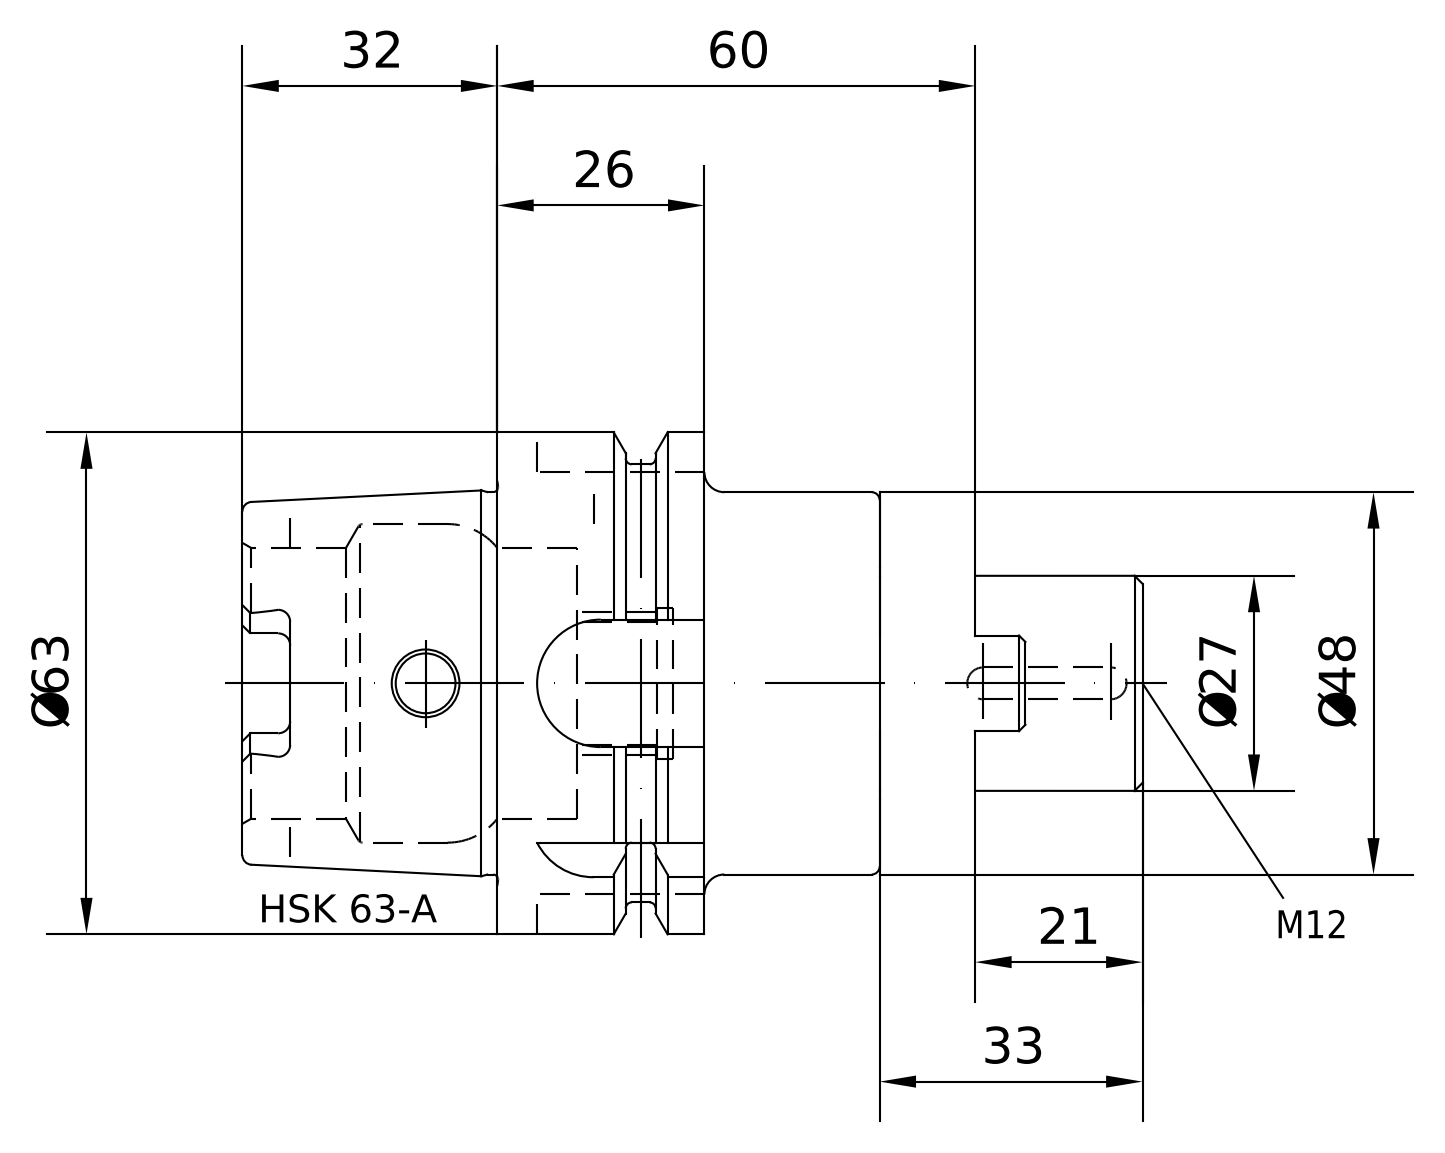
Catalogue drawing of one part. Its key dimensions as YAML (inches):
part_name: "A63-040-27; 85-200-27; A63-040-27_ASM"
step_written_by: "PRO/ENGINEER BY PARAMETRIC TECHNOLOGY CORPORATION, 2010430 (CONFIG_CONTROL_DESIGN)"
units: inches
bodies: {solids: 2, faces: 266, planar: 124, cylindrical: 64, other: 78}
overall_size: [4.449, 2.48, 2.48]
volume: 9.104
surface_area: 58.86
round_holes:
  - {diameter: 0.295, count: 1}
  - {diameter: 0.394, count: 1}
  - {diameter: 0.402, count: 1}
  - {diameter: 0.472, count: 1}
  - {diameter: 0.666, count: 1}
  - {diameter: 0.721, count: 1}
  - {diameter: 0.735, count: 1}
  - {diameter: 1.077, count: 1}
  - {diameter: 1.24, count: 1}
  - {diameter: 1.339, count: 1}
  - {diameter: 1.575, count: 1}
round_bosses_or_shafts:
  - {diameter: 2.48, count: 1}
  - {diameter: 2.165, count: 1}
  - {diameter: 1.891, count: 1}
  - {diameter: 1.89, count: 1}
  - {diameter: 1.063, count: 1}
  - {diameter: 0.709, count: 1}
partial_cylinders:
  - {radius: 0.059, count: 6}
  - {radius: 0.118, count: 4}
  - {radius: 0.138, count: 2}
  - {radius: 0.238, count: 1}
  - {radius: 0.315, count: 1}
  - {radius: 0.316, count: 1}
  - {radius: 0.355, count: 1}
face_to_face_distances: [1.89, 0.866, 1.024, 0.394, 2.362, 1.339, 0.472, 3.189, 1.26, 1.299]
